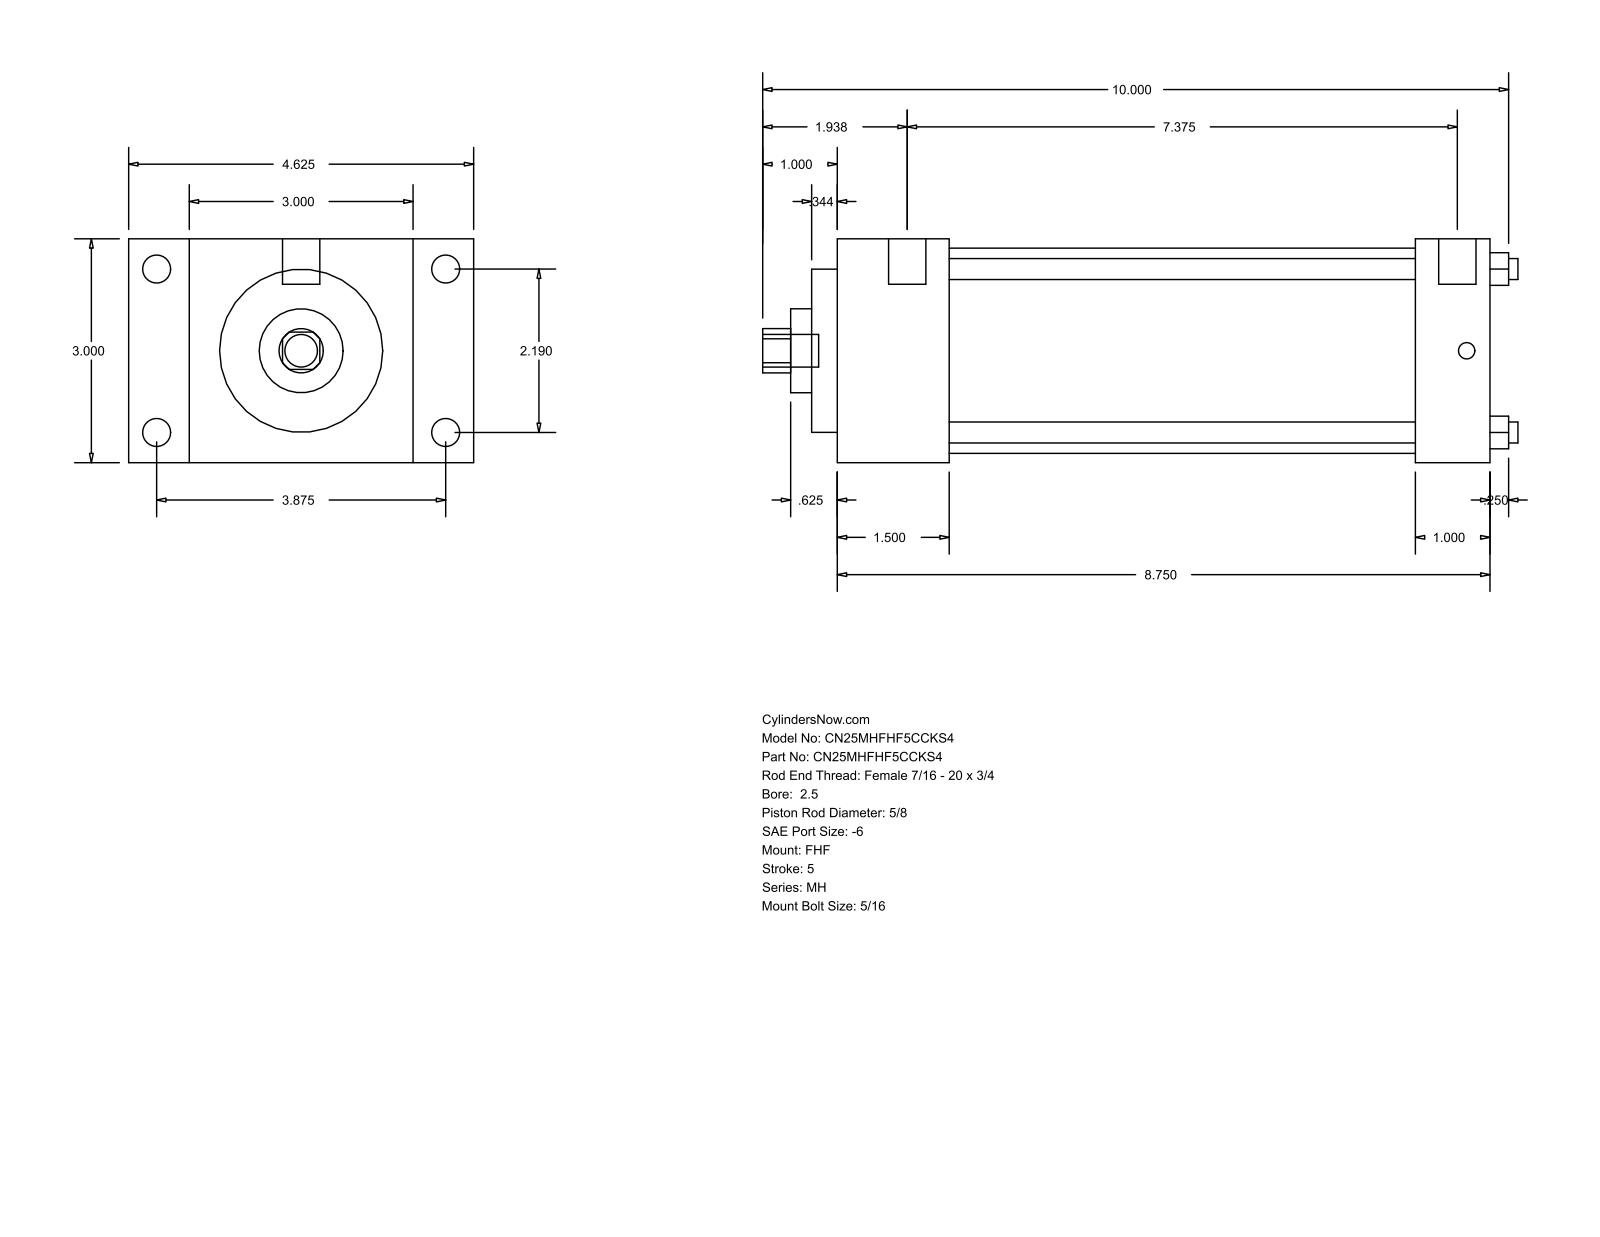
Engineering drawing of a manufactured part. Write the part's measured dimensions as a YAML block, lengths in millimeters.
part_name: "MH_FHF__0250_0.625"
step_written_by: "GSSL Pune (CONFIG_CONTROL_DESIGN)"
units: millimeters
bodies: {solids: 0, faces: 90, planar: 61, cylindrical: 29, other: 0}
overall_size: [257.18, 117.47, 76.2]
round_holes:
  - {diameter: 7.14, count: 4}
  - {diameter: 15.88, count: 1}
  - {diameter: 28.57, count: 1}
  - {diameter: 55.55, count: 1}
  - {diameter: 69.85, count: 1}
round_bosses_or_shafts:
  - {diameter: 9.53, count: 4}
  - {diameter: 5.56, count: 4}
  - {diameter: 12.7, count: 2}
  - {diameter: 11.11, count: 1}
partial_cylinders:
  - {radius: 7.54, count: 1}
face_to_face_distances: [76.2, 222.25, 38.1, 184.15, 20.64, 96.84, 117.48, 25.4, 196.85, 158.75]
hole_center_spacings: [39.33, 55.62, 78.66]
